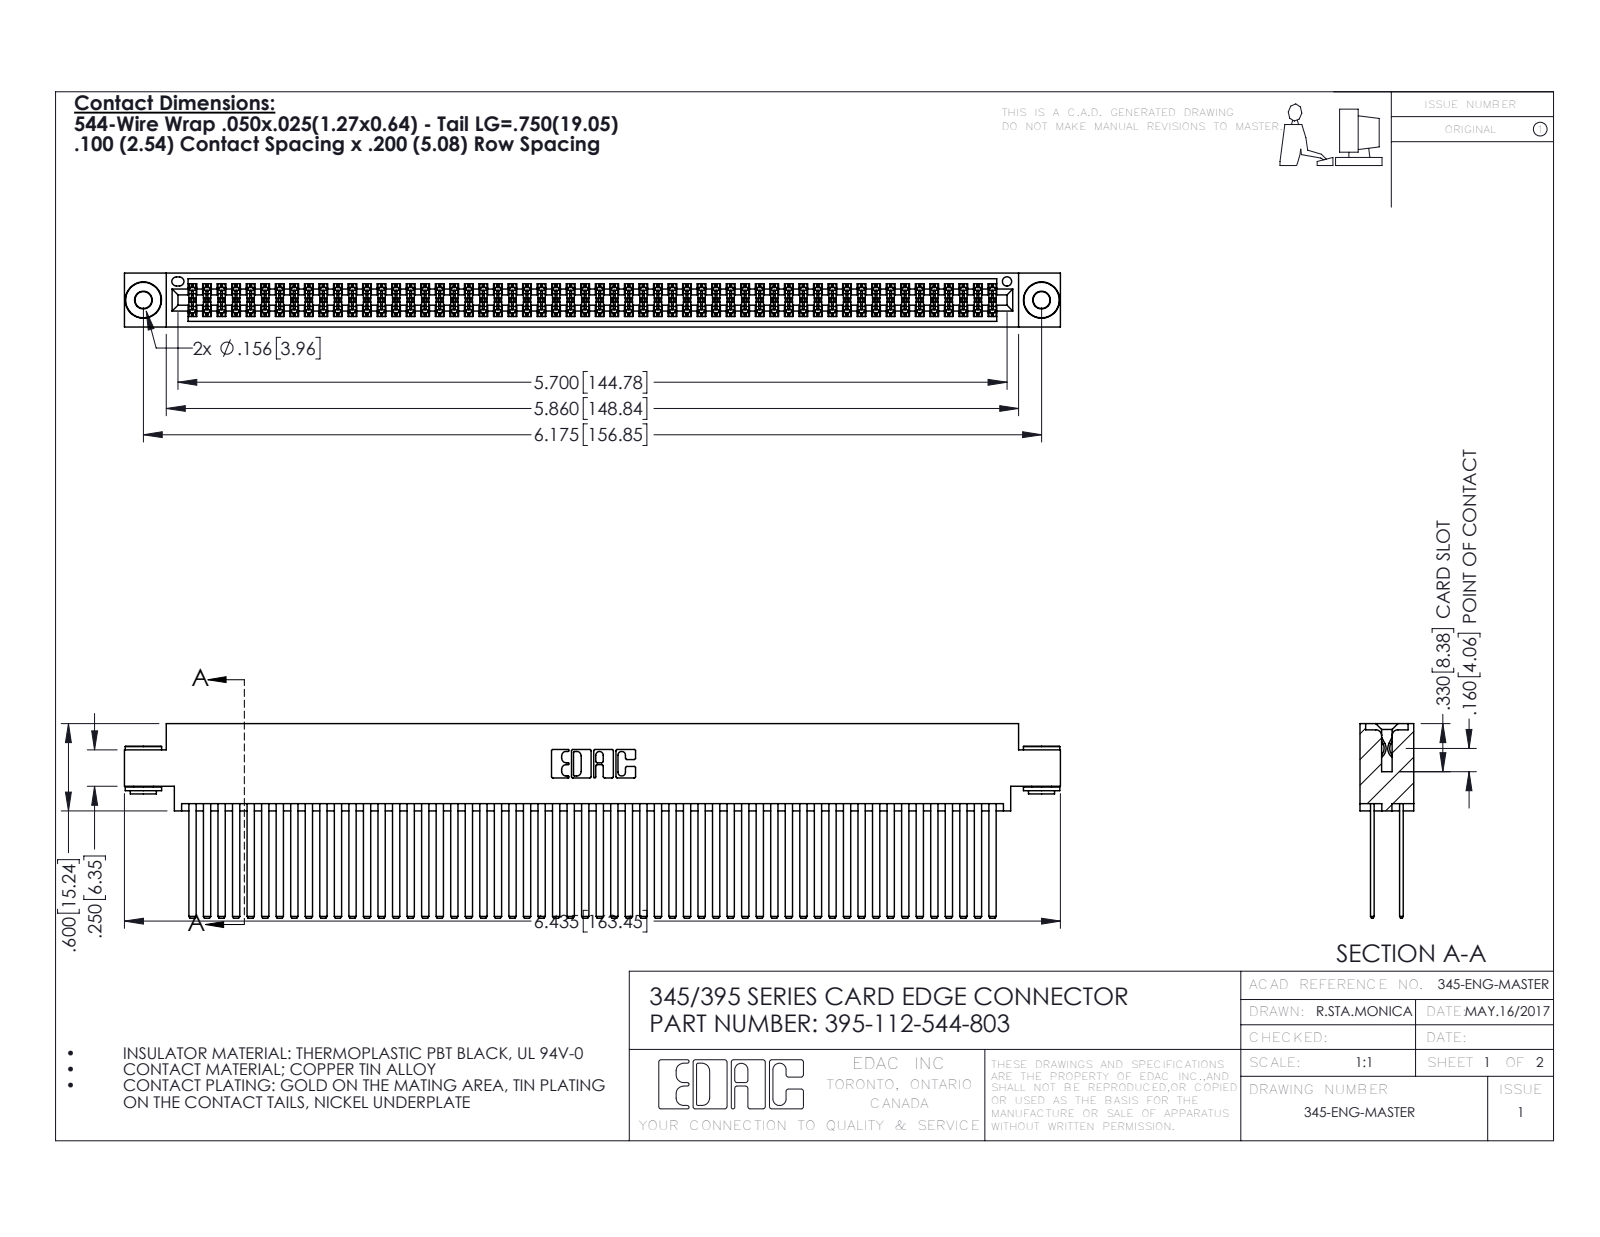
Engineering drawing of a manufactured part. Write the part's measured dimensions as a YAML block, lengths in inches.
part_name: "345-250-002_345-250-002-102; 345-292-001_345-293-144; 345 Part_0.170 Offset - 0.156 Dia-TH; 395-112-544-803"
step_written_by: "SolidWorks 2016 (CONFIG_CONTROL_DESIGN)"
units: inches
bodies: {solids: 115, faces: 5096, planar: 3342, cylindrical: 1746, other: 8}
overall_size: [6.435, 1.337, 0.37]
volume: 1.067
surface_area: 48.15
round_holes:
  - {diameter: 0.116, count: 2}
  - {diameter: 0.156, count: 2}
  - {diameter: 0.064, count: 1}
round_bosses_or_shafts:
  - {diameter: 0.25, count: 2}
  - {diameter: 0.18, count: 2}
  - {diameter: 0.136, count: 2}
partial_cylinders:
  - {radius: 0.006, count: 168}
  - {radius: 0.01, count: 22}
  - {radius: 0.007, count: 6}
  - {radius: 0.031, count: 6}
  - {radius: 0.026, count: 3}
  - {radius: 0.014, count: 2}
  - {radius: 0.019, count: 2}
  - {radius: 0.022, count: 2}
face_to_face_distances: [0.2, 0.025, 0.072, 0.098, 0.272, 0.298, 0.225, 0.175, 0.37, 0.15]
hole_center_spacings: [0.27, 5.939, 6.175]
